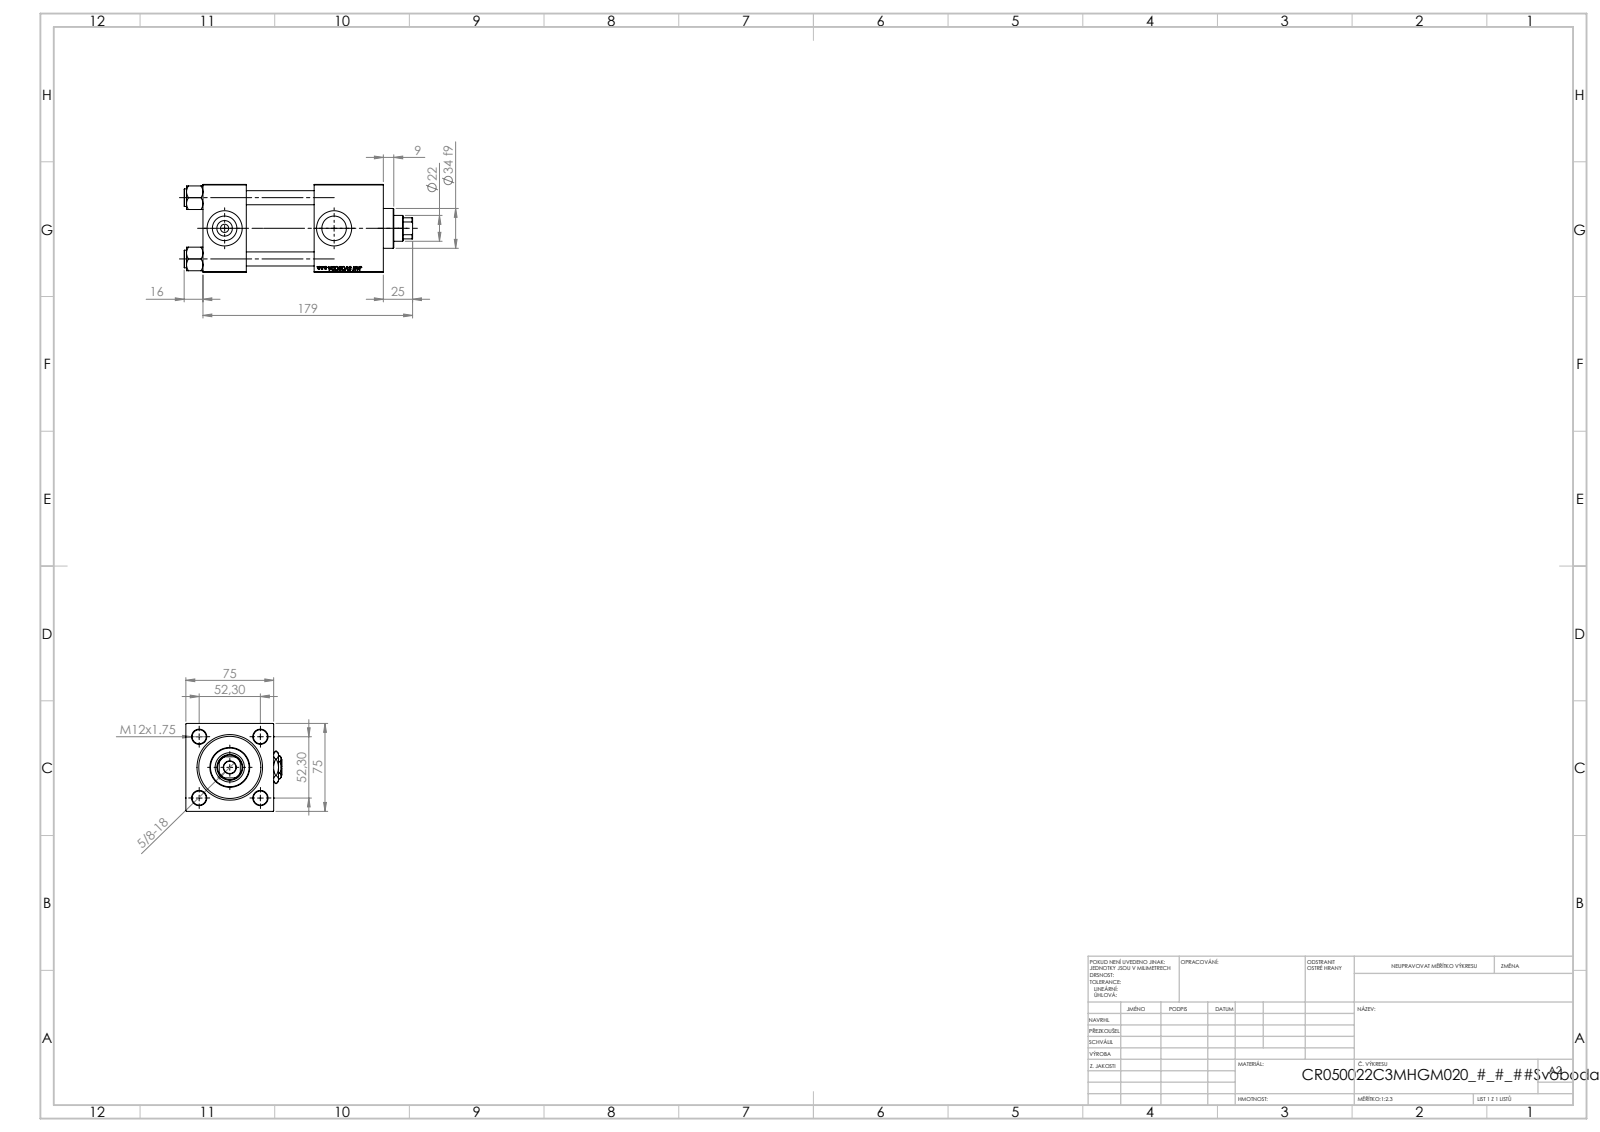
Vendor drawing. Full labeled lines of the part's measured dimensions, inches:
Part name (STEP PRODUCT): V215CR_VCP_C; V215_VC_A; V215CR_C_Body; NUT_M5_C (+2 more)
STEP written by: SolidWorks 2019 (CONFIG_CONTROL_DESIGN)
Units: inches
Bodies: 13 solids, 1249 faces (573 planar, 98 cylindrical, 578 other)
Overall size (bounding box): 7.677 × 3.239 × 2.953
Volume: 39.78 in³ · Surface area: 235.2 in²
Round holes (diameter × count): ⌀0.472 ×4, ⌀0.276 ×2, ⌀0.825 ×2, ⌀1.181 ×2, ⌀0.413 ×1, ⌀0.866 ×1, ⌀0.984 ×1, ⌀1.614 ×1, ⌀1.969 ×1, ⌀2.087 ×1
Round bosses / shafts (diameter × count): ⌀0.591 ×4, ⌀2.205 ×1, ⌀1.339 ×1
Partial cylindrical surfaces — rounded edges, fillets, slot ends (radius × count): R0.413 ×1
Main face-to-face distances: 2.953, 1.457, 6.063, 4.606, 3.74, 2.283, 2.323, 4.933, 3.476, 1.193
Hole centre spacings: 1.456, 2.059, 2.912, 3.681
